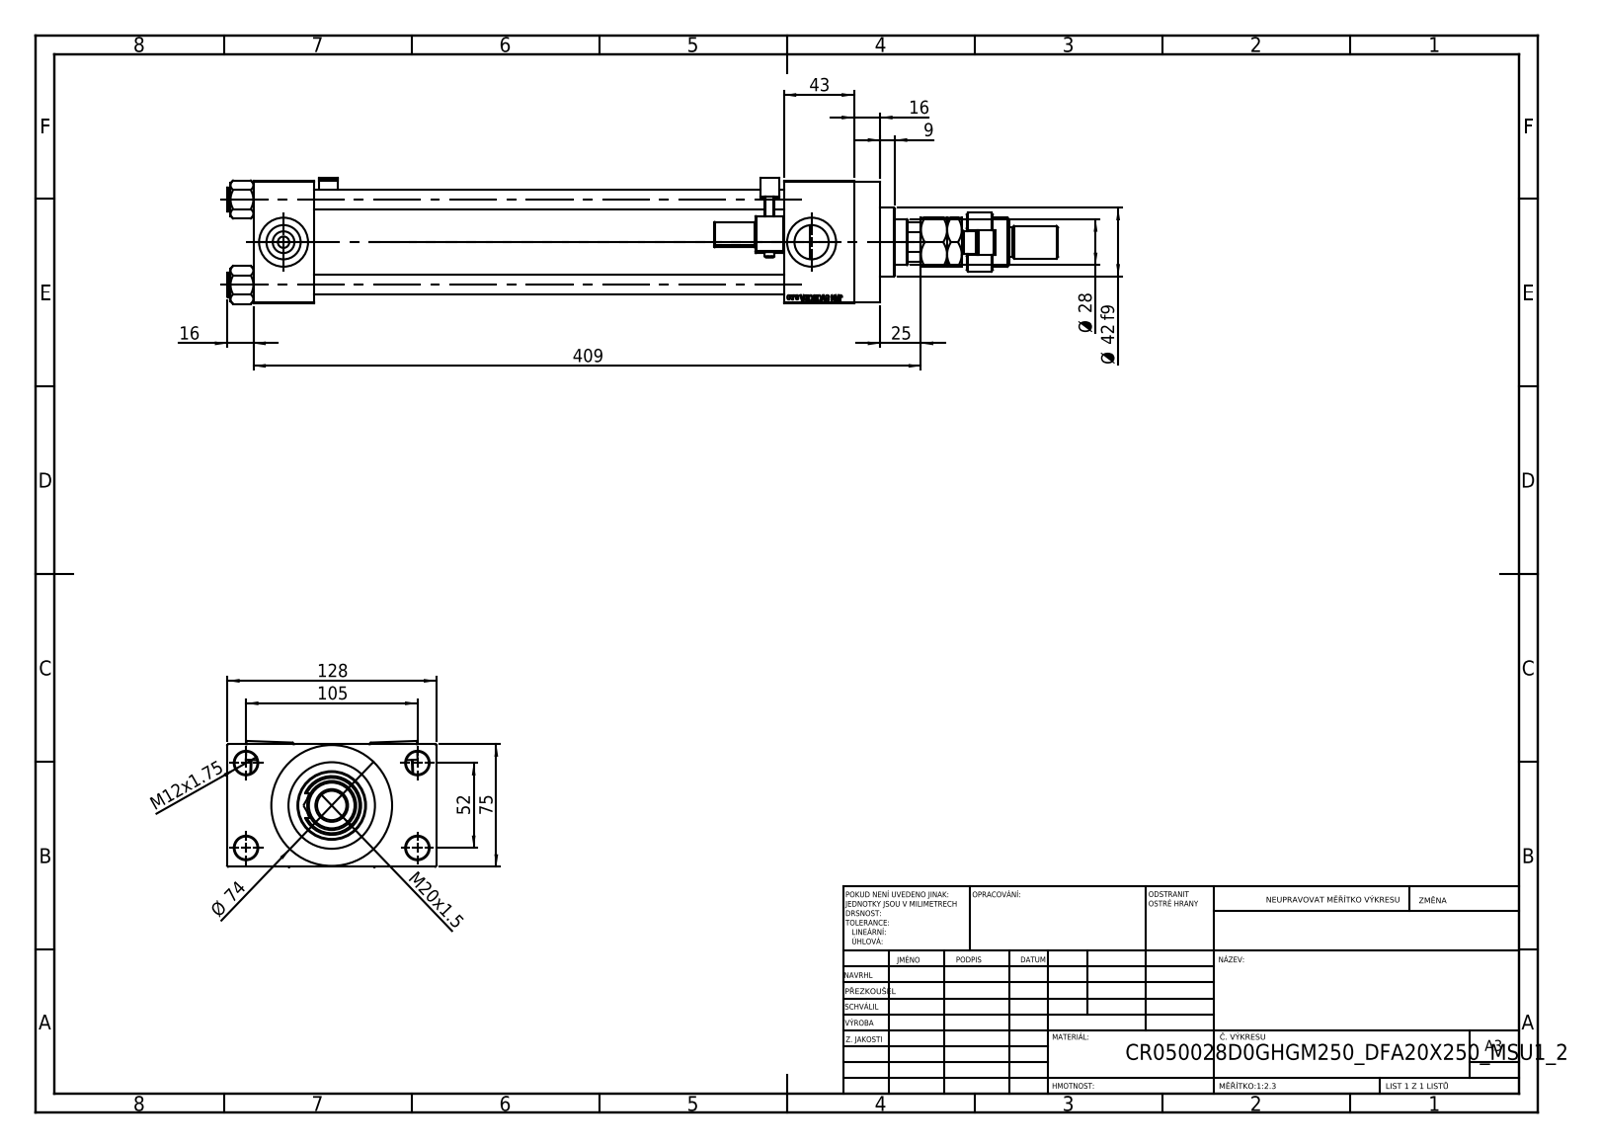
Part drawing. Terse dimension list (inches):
name: V215CR_D_Body; NUT_M5_D; V215CR_D_TYCINKA; V215_VC_A (+4 more)
written by: SolidWorks 2019 (CONFIG_CONTROL_DESIGN)
unit: in
bodies: 15 solids, 1342 faces (583 planar, 161 cylindrical, 598 other)
size: 20.039 × 5.039 × 3.043
volume: 76.71 in³; area: 507.8 in²
holes: 4× ⌀0.472, 4× ⌀0.551, 2× ⌀0.276, 2× ⌀0.825, 2× ⌀1.181, 1× ⌀0.728, 1× ⌀1.102, 1× ⌀1.22, 1× ⌀1.614, 1× ⌀1.969, 1× ⌀2.087
bosses: 4× ⌀0.591, 2× ⌀0.236, 1× ⌀2.913, 1× ⌀2.205, 1× ⌀1.654, 1× ⌀1.417, 1× ⌀1.181, 1× ⌀0.866
rounds: 48× R0.02, 2× R0.039, 2× R0.098, 2× R0.157, 1× R0.295, 1× R0.472, 1× R0.531
face distances: 2.953, 11.339, 1.457, 12.795, 1.043, 3.996, 1.693, 14.488, 13.031, 0.63
hole spacings: 1.037, 1.456, 2.059, 2.3, 2.307, 3.096, 3.715, 2.047
